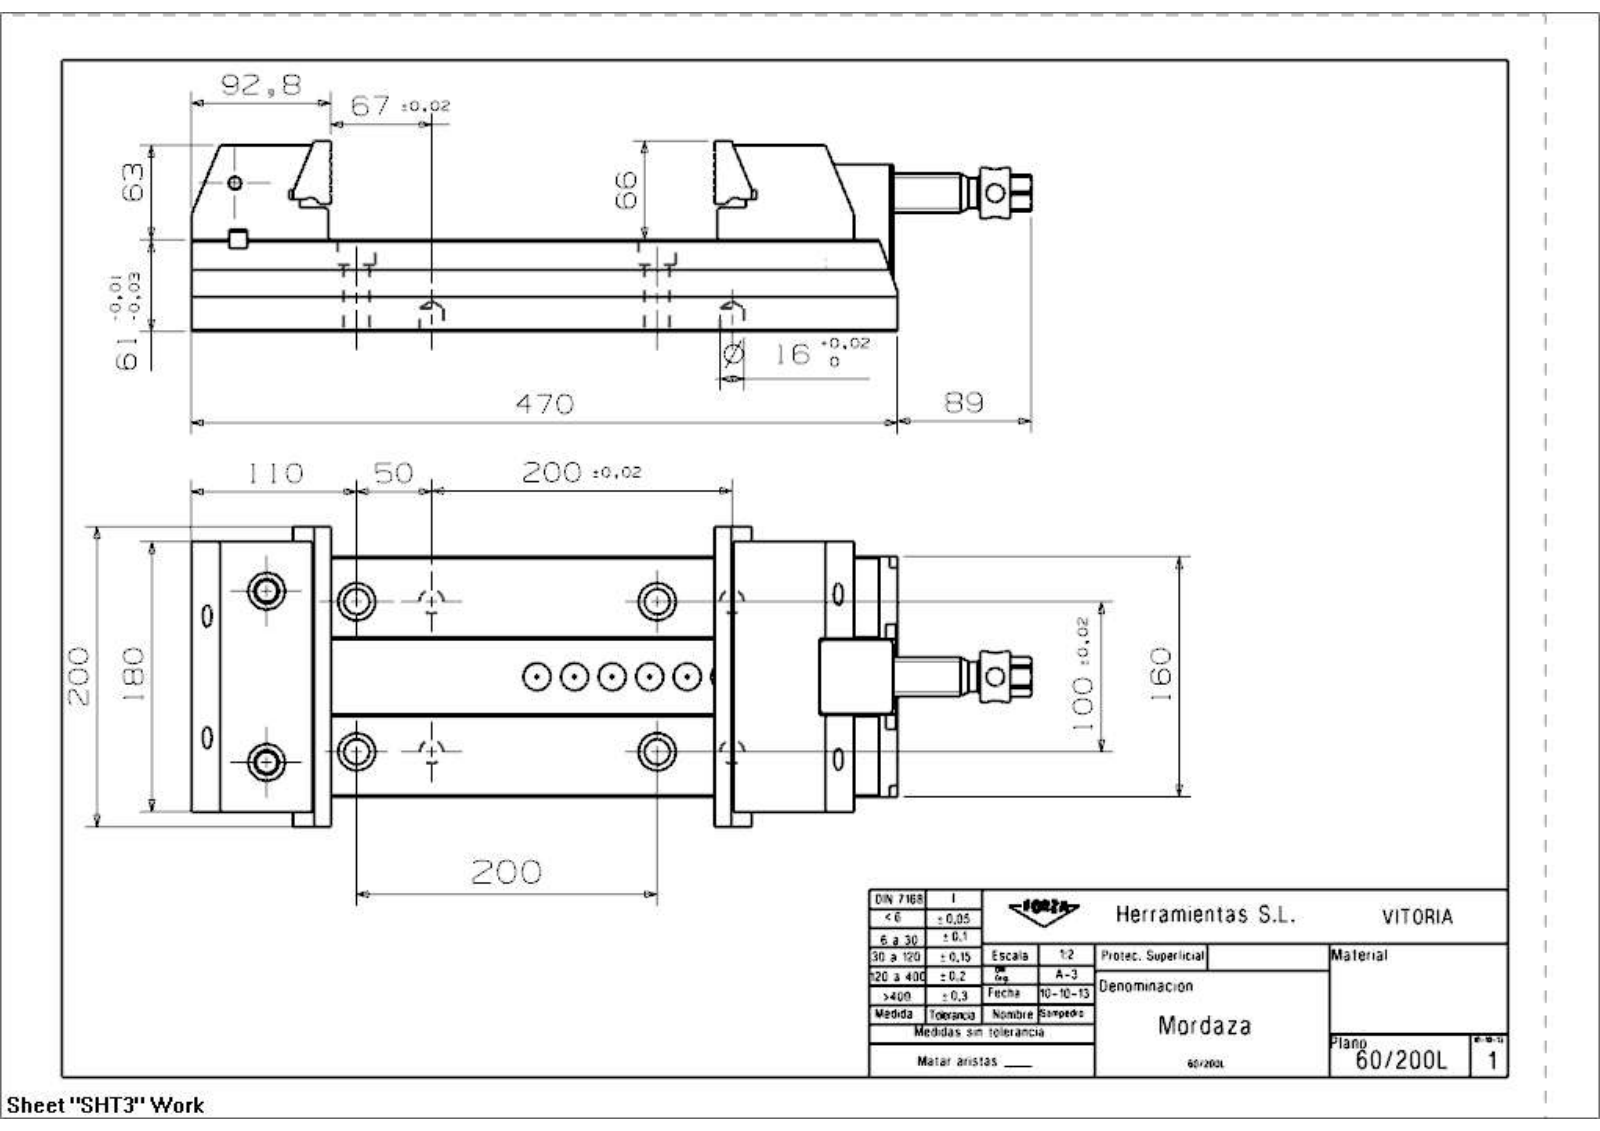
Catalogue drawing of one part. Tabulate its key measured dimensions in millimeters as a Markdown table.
| quantity | value |
| --- | --- |
| part name | 60_175L_Mordaza |
| STEP written by | SIEMENS PLM Software NX 7.5 (CONFIG_CONTROL_DESIGN) |
| units | millimeters |
| bodies | 12 solids, 453 faces (289 planar, 97 cylindrical, 67 other) |
| overall size | 571 × 175 × 115.4 |
| volume | 4 043 000 mm³ |
| surface area | 533 165 mm² |
| round holes (diameter × count) | 15 × 6, 8.78 × 5, 16 × 5, 17 × 5, 25 × 5, 6.99 × 4, 8.5 × 4, 10 × 4, 10.58 × 4, 13 × 4, 19 × 4, 12 × 2 |
| round bosses / shafts (diameter × count) | 34 × 1, 33.8 × 1, 26 × 1, 20 × 1, 16.5 × 1 |
| partial cylindrical surfaces (radius × count) | 20 × 4, 1.6 × 2, 6 × 2, 7 × 2, 4 × 1, 9 × 1, 10.5 × 1, 12.5 × 1 |
| main face-to-face distances | 56.8, 32.2, 24.6, 102.5, 10, 42.5, 32.5, 135, 52.5, 112.5 |
| hole center spacings | 78.5, 100, 111.8, 6.5, 6.51, 50, 72, 85 |
